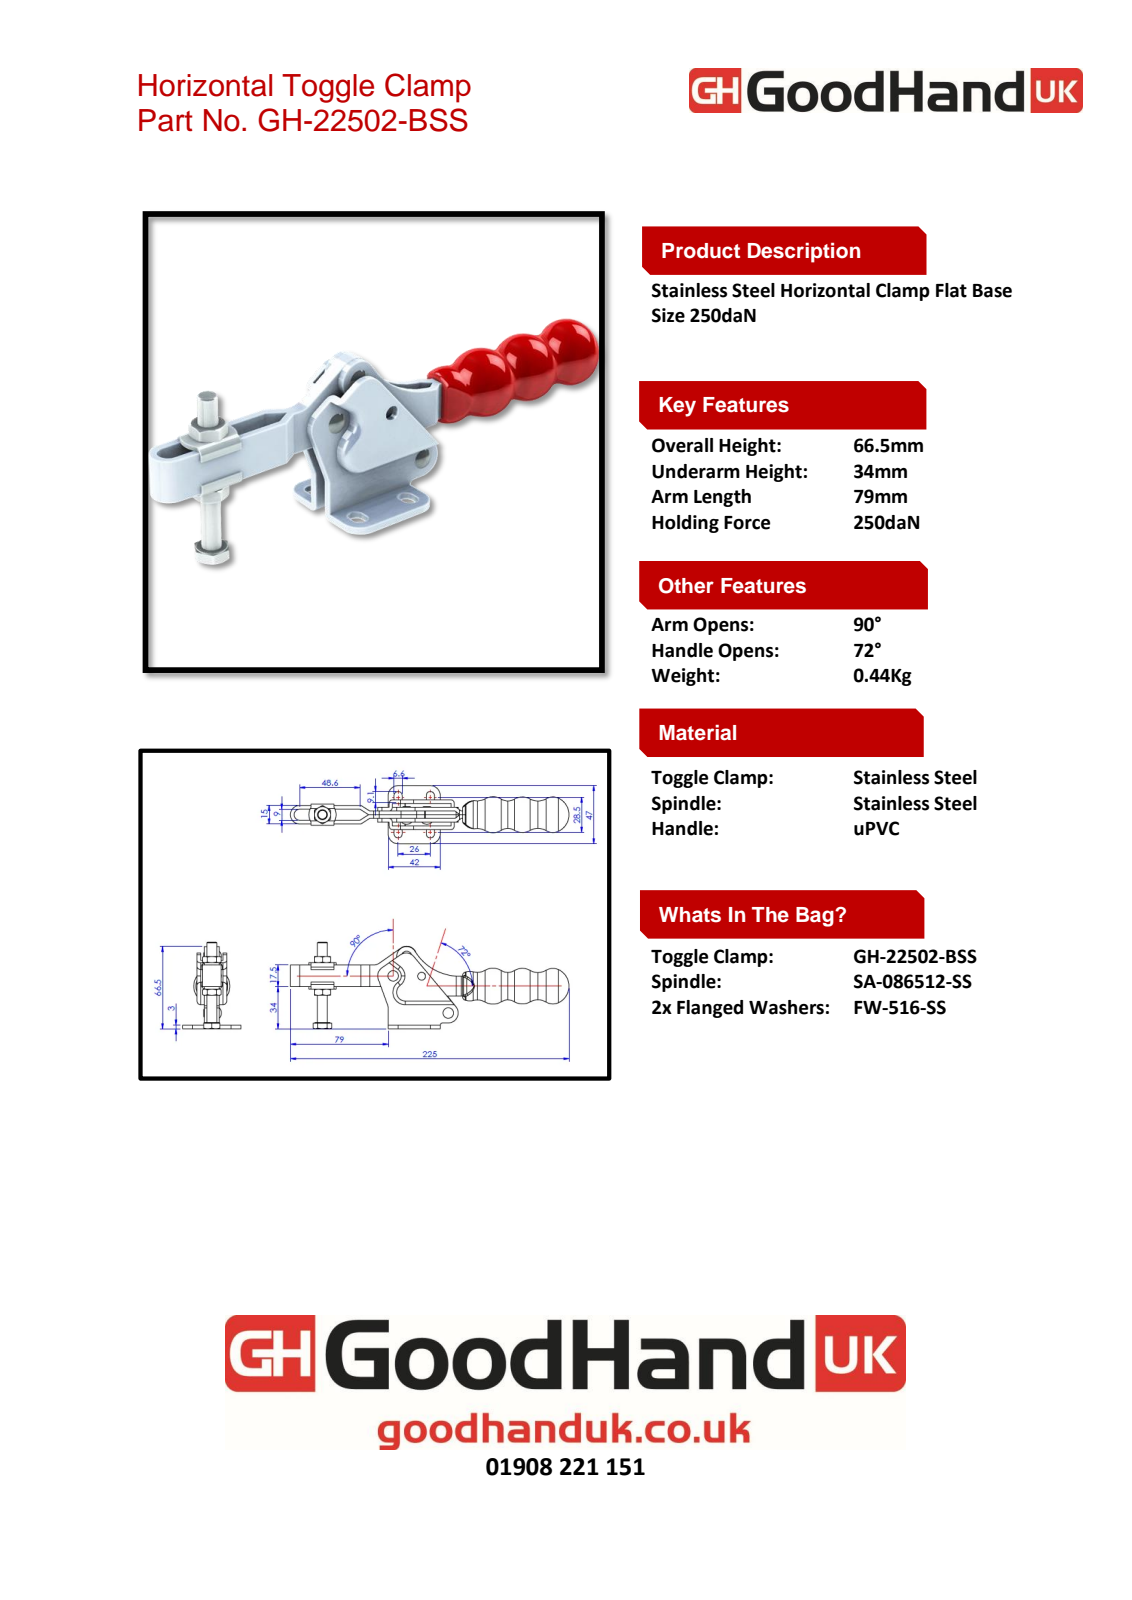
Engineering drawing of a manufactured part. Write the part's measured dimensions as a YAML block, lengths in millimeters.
part_name: "Group5^EMC22502B; Group4^EMC22502B; 122502B08-1^EMC22502B; Group3^EMC22502B (+2 more)"
step_written_by: "SolidWorks 2016 (AUTOMOTIVE_DESIGN)"
units: millimeters
bodies: {solids: 5, faces: 332, planar: 145, cylindrical: 111, other: 76}
overall_size: [225.06, 66.75, 47]
volume: 93389
surface_area: 45273
round_holes:
  - {diameter: 4, count: 4}
round_bosses_or_shafts:
  - {diameter: 12.5, count: 1}
  - {diameter: 8, count: 1}
  - {diameter: 7.2, count: 1}
  - {diameter: 6.35, count: 1}
partial_cylinders:
  - {radius: 8, count: 10}
  - {radius: 3.3, count: 8}
  - {radius: 1.2, count: 4}
  - {radius: 3.6, count: 4}
  - {radius: 10, count: 4}
  - {radius: 1, count: 3}
  - {radius: 11.04, count: 2}
  - {radius: 35.27, count: 2}
face_to_face_distances: [3, 6, 9, 12, 4.5, 1.5, 15, 7.5, 16.5, 13.5]
hole_center_spacings: [19.08, 27.73, 28.52, 29.07, 53.67, 56.77]
